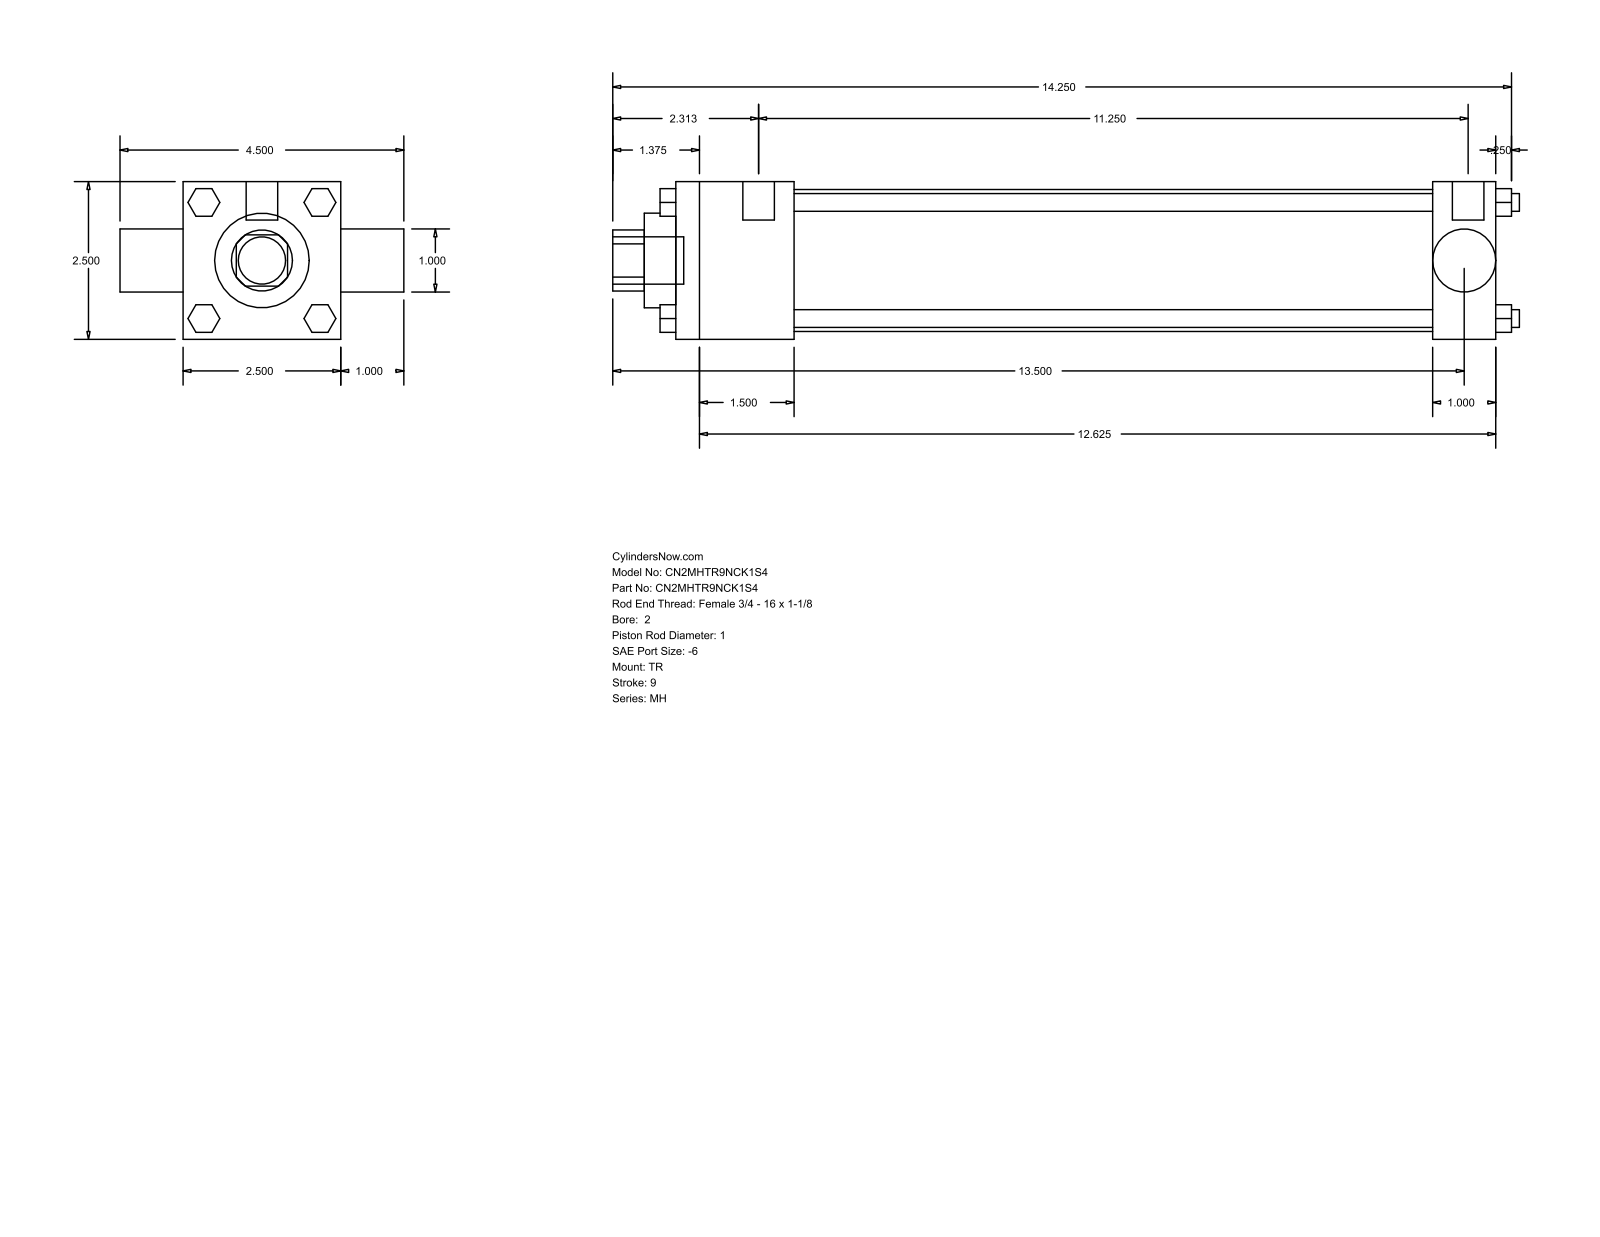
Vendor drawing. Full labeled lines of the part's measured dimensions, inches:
Part name (STEP PRODUCT): MH_TR__0200_1
STEP written by: GSSL Pune (CONFIG_CONTROL_DESIGN)
Units: inches
Bodies: 0 solids, 120 faces (92 planar, 28 cylindrical, 0 other)
Overall size (bounding box): 14.375 × 4.5 × 2.5
Round holes (diameter × count): ⌀0.998 ×1, ⌀1 ×1, ⌀1.5 ×1, ⌀2.25 ×1
Round bosses / shafts (diameter × count): ⌀0.281 ×4, ⌀0.219 ×3, ⌀0.5 ×2, ⌀0.75 ×1
Partial cylindrical surfaces — rounded edges, fillets, slot ends (radius × count): R0.484 ×1
Main face-to-face distances: 2.5, 13, 1, 1.875, 12, 10.125, 11.125, 3.5, 13.5, 0.25
